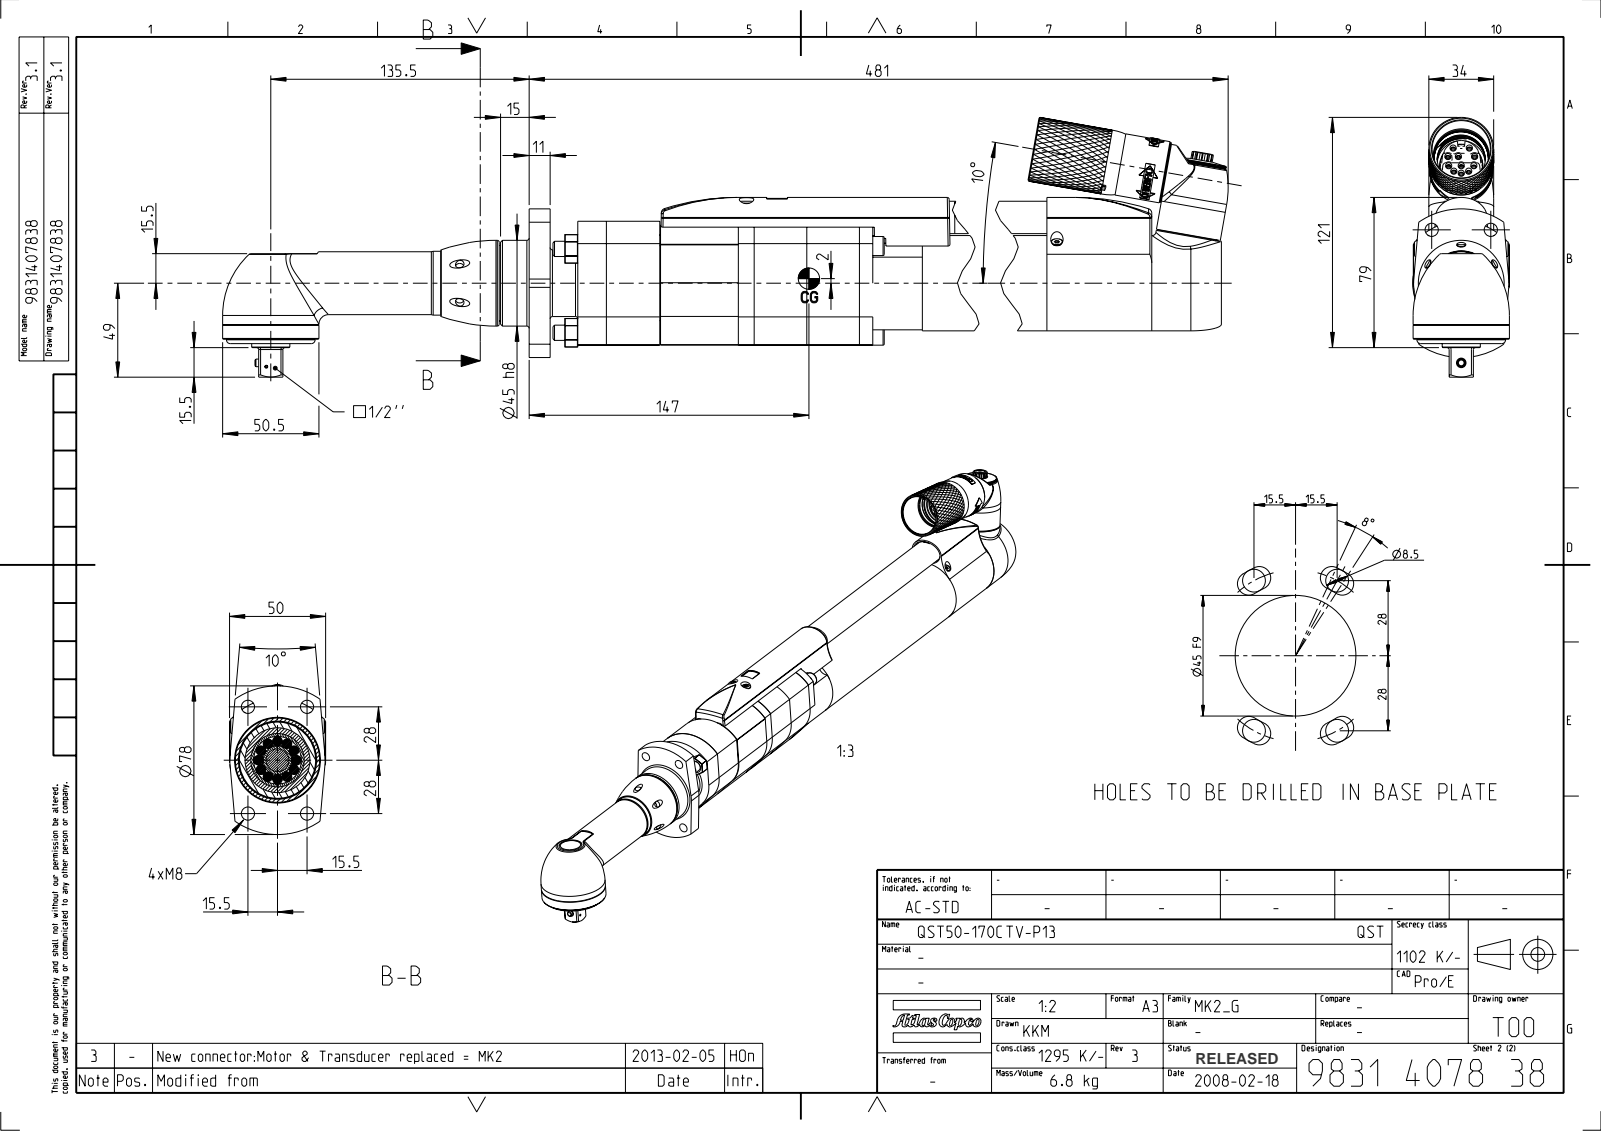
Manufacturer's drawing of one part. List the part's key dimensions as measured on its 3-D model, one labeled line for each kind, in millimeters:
Part name (STEP PRODUCT): 4230260202; 4230260212_ASM; 4230265900; 0219110017 (+8 more)
STEP written by: PRO/ENGINEER BY PARAMETRIC TECHNOLOGY CORPORATION, 2012420 (CONFIG_CONTROL_DESIGN)
Units: millimetres
Bodies: 38 solids, 5301 faces (2078 planar, 1680 cylindrical, 1543 other)
Overall size (bounding box): 642 × 136.29 × 50.5
Volume: 768 254 mm³ · Surface area: 373 520 mm²
Round holes (diameter × count): ⌀4.5 ×13, ⌀2.64 ×11, ⌀3.27 ×11, ⌀3.6 ×11, ⌀3.3 ×7, ⌀3.24 ×6, ⌀4.92 ×4, ⌀6.92 ×4, ⌀8 ×4, ⌀9 ×4, ⌀1.4 ×3, ⌀1.5 ×3
Round bosses / shafts (diameter × count): ⌀8 ×8, ⌀4 ×5, ⌀3 ×5, ⌀6 ×4, ⌀5 ×4, ⌀34 ×3, ⌀10 ×3, ⌀2.5 ×3
Partial cylindrical surfaces — rounded edges, fillets, slot ends (radius × count): R1 ×89, R0.2 ×62, R0.1 ×53, R0.5 ×35, R0.29 ×12, R0.51 ×12, R2 ×7, R32.5 ×5
Main face-to-face distances: 27.6, 11, 33, 15, 165.7, 50, 195.2, 29.5, 268, 375.2
Hole centre spacings: 7.16, 7.41, 7.43, 18.26, 32, 7.42, 19.5, 2.12
